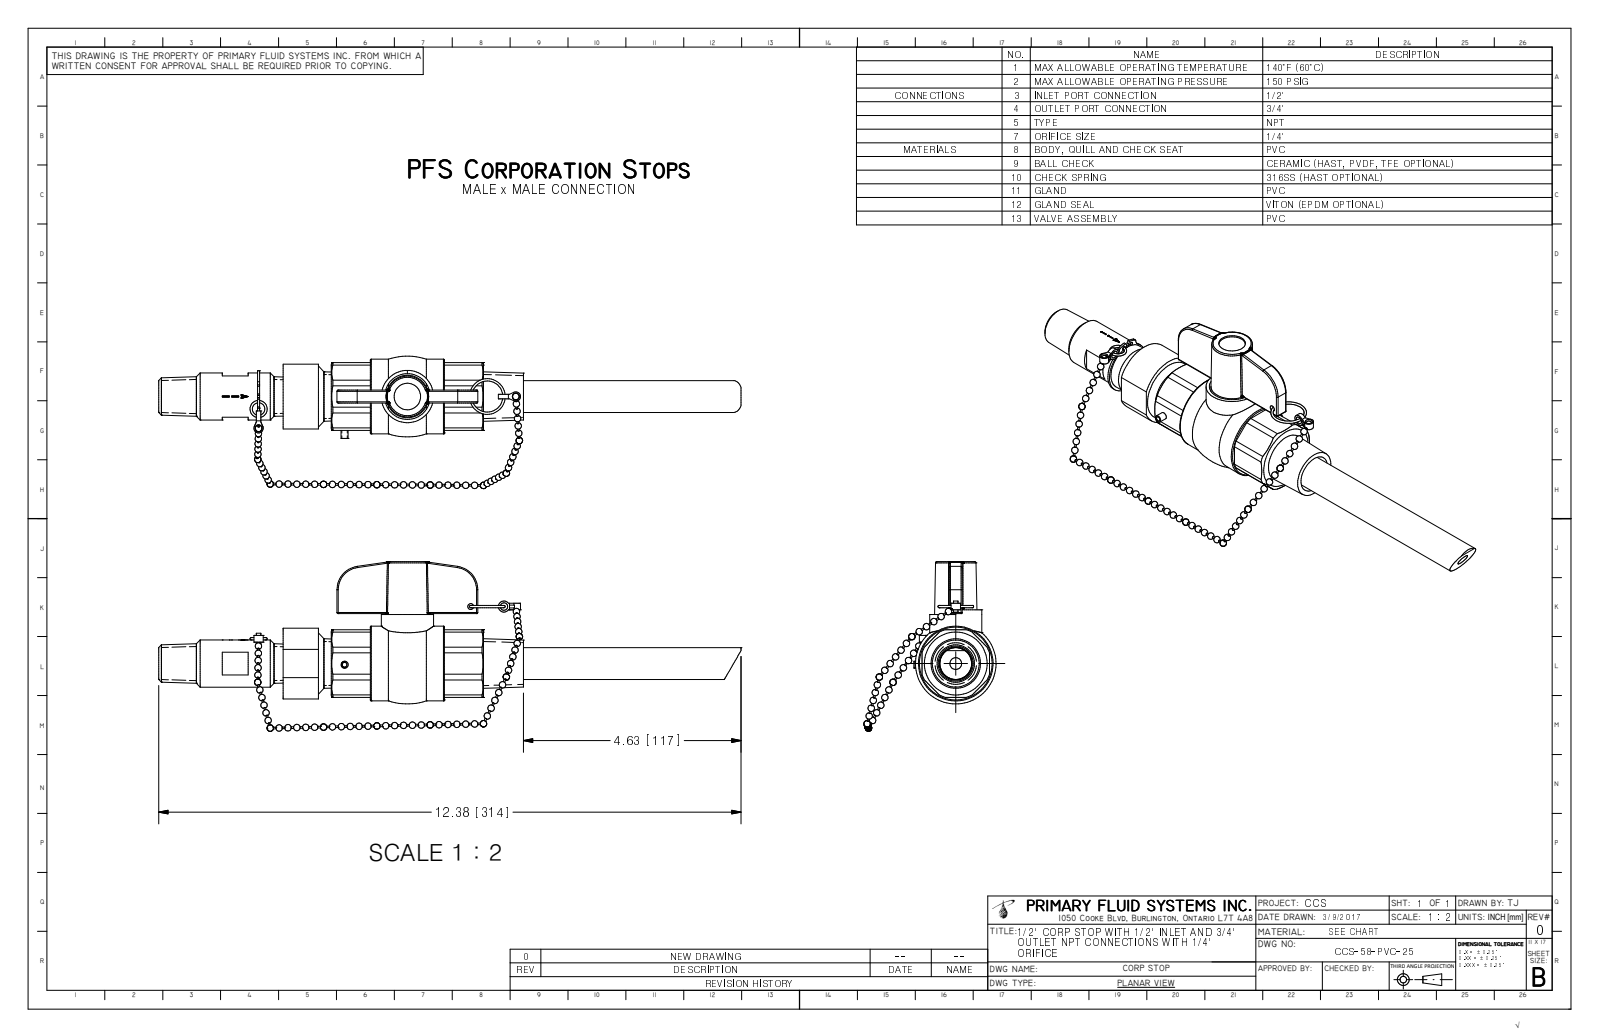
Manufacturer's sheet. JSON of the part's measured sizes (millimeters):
{"part_name": "CCS-58-PVC-25_R0", "step_written_by": "Autodesk Inventor 2009 (AUTOMOTIVE_DESIGN)", "units": "millimeters", "bodies": {"solids": 1, "faces": 392, "planar": 115, "cylindrical": 59, "other": 218}, "overall_size": [314.5, 91.4, 71.4], "volume_mm3": 208100, "surface_area_mm2": 46040, "round_holes": [[2, 1], [3.8, 1], [6.4, 1], [11.9, 1], [14.2, 1], [14.3, 1], [24.6, 1]], "round_bosses_or_shafts": [[40.3, 1], [28.2, 1], [27.8, 1], [25.4, 1], [22.9, 1], [17.1, 1], [14.2, 1]], "partial_cylinders_radius": [[0.6, 12], [1.1, 2], [4, 2], [12.7, 2], [11.5, 1], [11.8, 1], [12.7, 1], [15.6, 1]], "face_to_face_distances": [36.4, 0.8, 14, 7, 21, 14.7, 21.7, 35.7, 6.4, 26], "hole_center_spacings": [13.6]}
